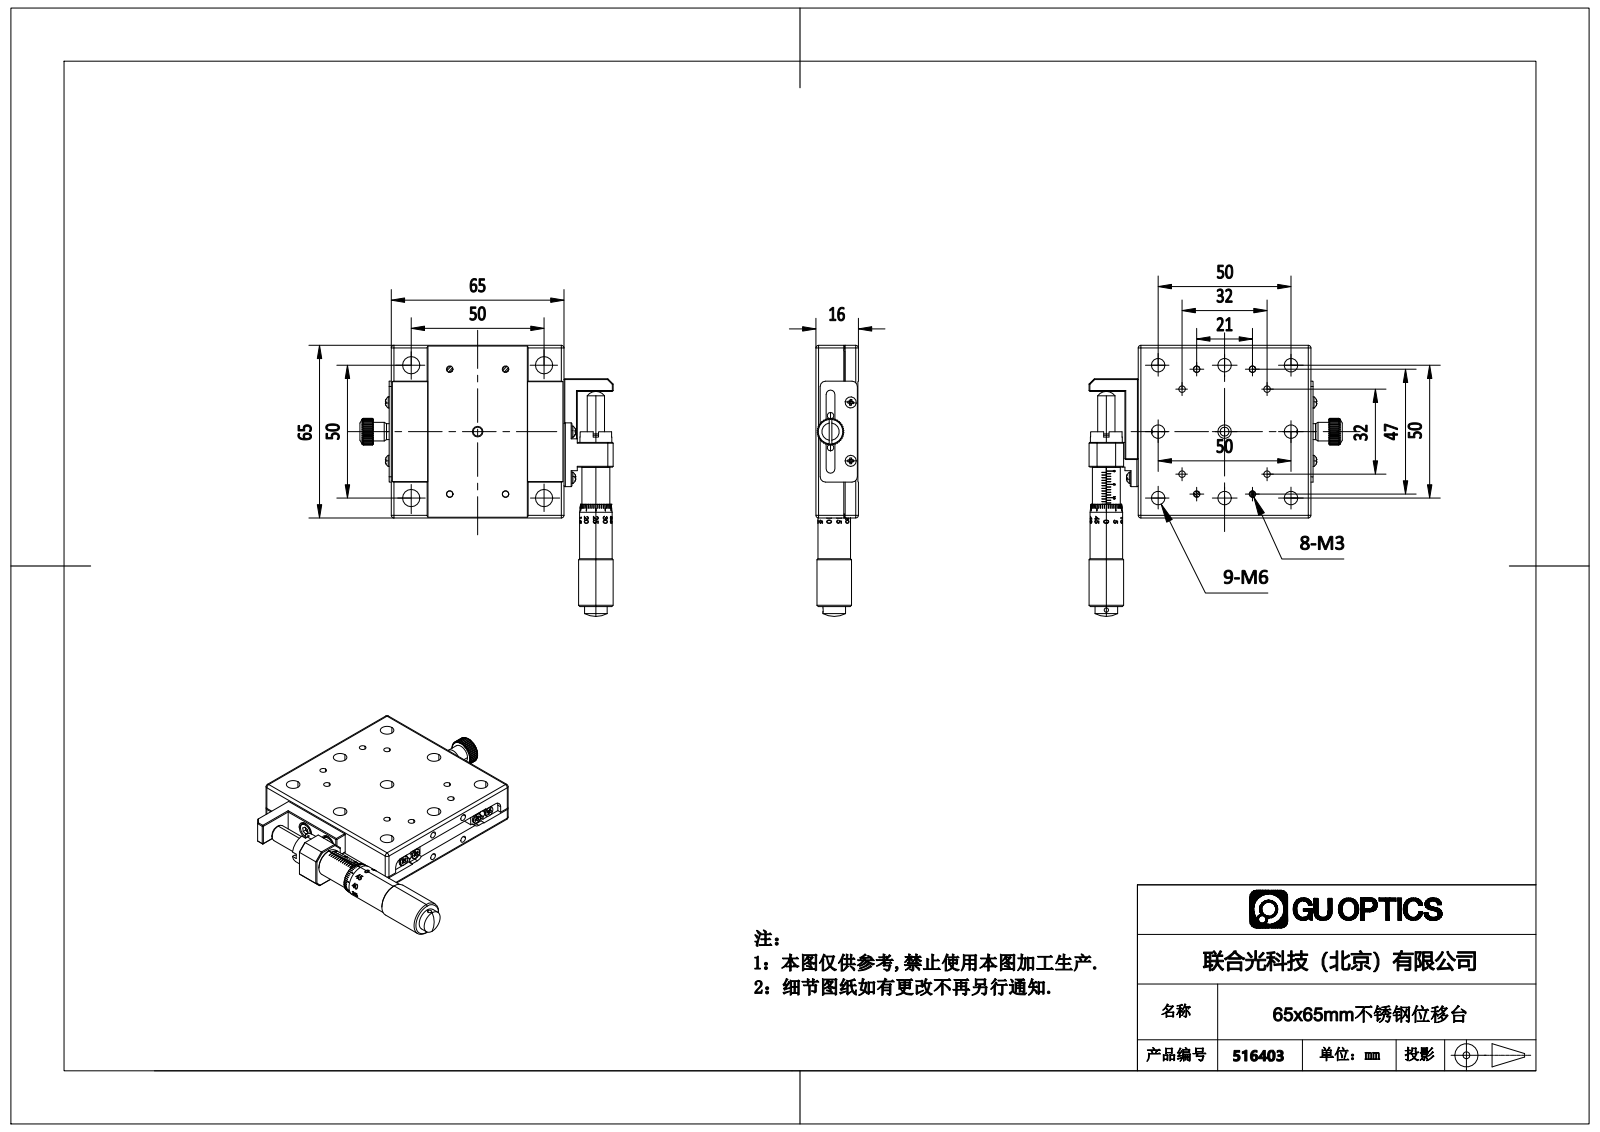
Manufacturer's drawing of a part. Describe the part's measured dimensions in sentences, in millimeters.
The part is named "A1833-243-SB". Its 3-D file was written by "SolidWorks 2020 (CONFIG_CONTROL_DESIGN)". It is 51 solids with 4601 faces: 685 planar, 1887 cylindrical and 2029 other. Overall it measures 102.05 by 95.3 by 16 millimeters. Its volume is 63 054 cubic millimeters and its surface area 42 412 square millimeters. Round holes: 15 of diameter 2.5, 9 of diameter 5.1, 5 of diameter 1.6, 5 of diameter 2.05, 5 of diameter 6.5, 4 of diameter 10.5, 3 of diameter 3.4, 2 of diameter 2.9, 2 of diameter 3, 2 of diameter 6, 1 of diameter 3.2, 1 of diameter 3.3. Round bosses or shafts: 678 of diameter 0.5, 8 of diameter 2, 7 of diameter 3, 5 of diameter 4, 4 of diameter 4.2, 4 of diameter 3.5, 4 of diameter 2.5, 4 of diameter 2.4. Partial cylindrical surfaces (rounded edges, fillets, slot ends): 12 of radius 1, 8 of radius 1.75, 4 of radius 2, 4 of radius 2.75, 2 of radius 1.65, 1 of radius 5. The main face-to-face distances are 5, 5.5, 4.8, 6, 10.7, 15.7, 5.9, 0.5, 9.8, 10.5. The hole center spacings are 25, 18.36, 35.36, 41.98, 44.01, 55.9, 50, 6.4.
